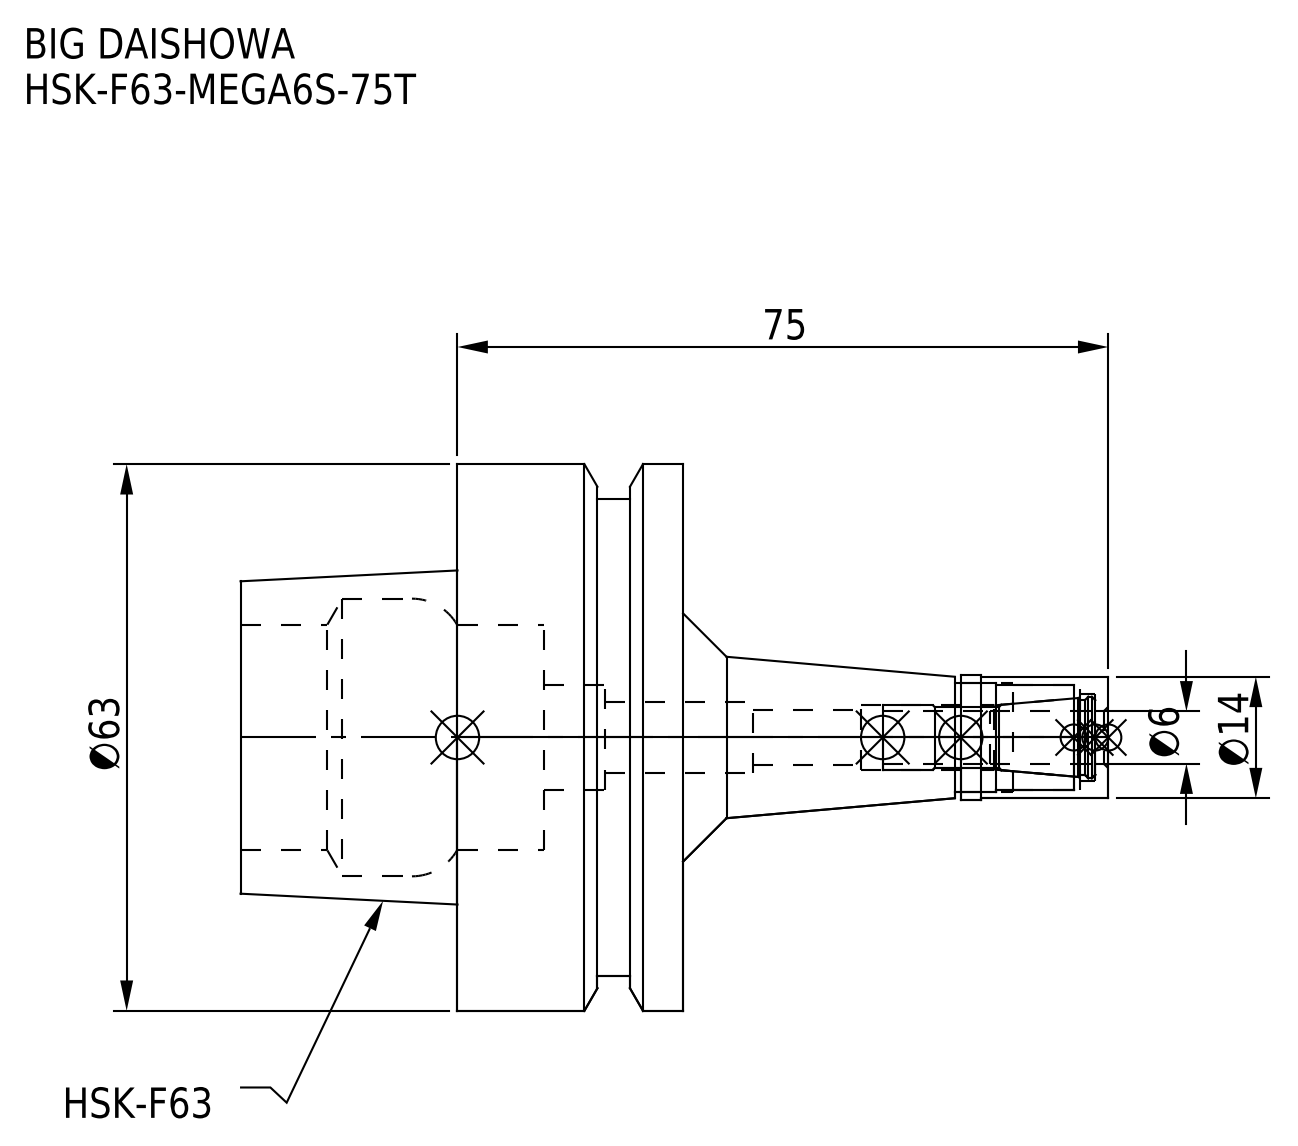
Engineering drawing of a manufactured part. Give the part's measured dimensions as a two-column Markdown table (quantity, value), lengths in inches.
| quantity | value |
| --- | --- |
| part name | HSK-F63-MEGA6S-75T-060.stp; HSK-F63-MEGA6S-75T; MGN6S_1.stp; HSK-F63-MEGA6S-75T-060-FreeParts (+3 more) |
| STEP written by | SolidWorks 2019 (CONFIG_CONTROL_DESIGN) |
| units | inches |
| bodies | 2 solids, 74 faces (18 planar, 38 cylindrical, 18 other) |
| overall size | 3.937 × 2.48 × 2.48 |
| volume | 5.476 in³ |
| surface area | 36.35 in² |
| round holes (diameter × count) | 0.24 × 1, 0.252 × 1, 0.291 × 1, 0.325 × 1, 0.394 × 1, 0.472 × 1, 0.492 × 1, 1.024 × 1, 1.26 × 1 |
| round bosses / shafts (diameter × count) | 2.48 × 1, 2.165 × 1, 0.563 × 1, 0.551 × 1 |
| main face-to-face distances | 1.024, 2.008, 0.984, 0.632, 0.392, 1.376, 0.389, 0.243, 0.635, 1.619 |
